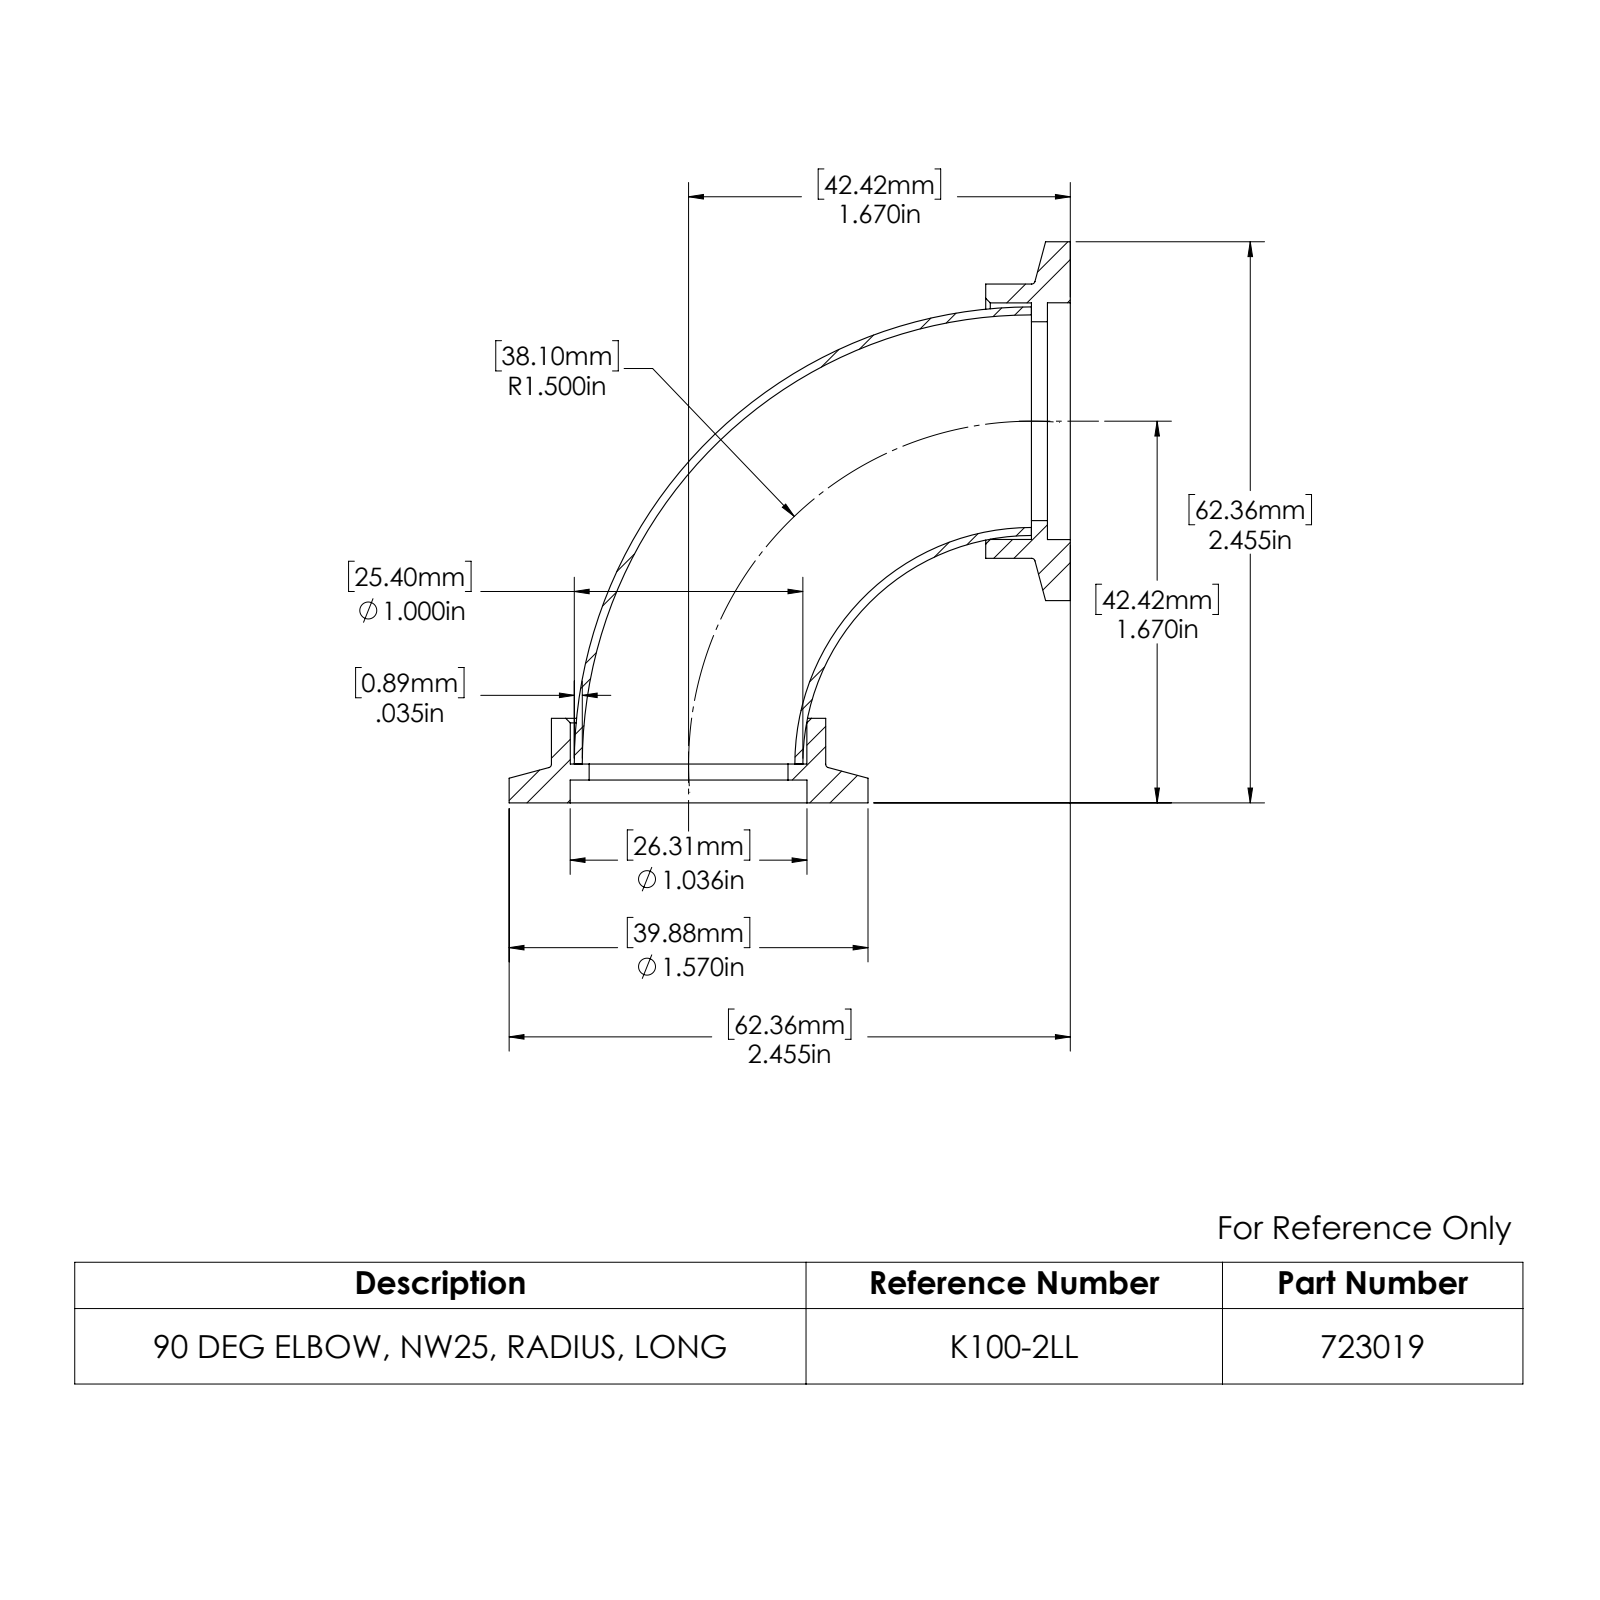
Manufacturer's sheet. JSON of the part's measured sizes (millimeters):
{"part_name": "403541; 723019; 972301", "step_written_by": "SolidWorks 2022 (AUTOMOTIVE_DESIGN)", "units": "millimeters", "bodies": {"solids": 3, "faces": 42, "planar": 10, "cylindrical": 20, "other": 12}, "overall_size": [62.36, 62.36, 39.88], "volume_mm3": 11647, "surface_area_mm2": 16063, "round_holes": [[22.1, 2], [26.29, 2], [26.31, 2]], "round_bosses_or_shafts": [[39.88, 2], [30.48, 2]], "face_to_face_distances": [4.32, 9.4, 5.08, 2.54, 1.78, 6.86]}
